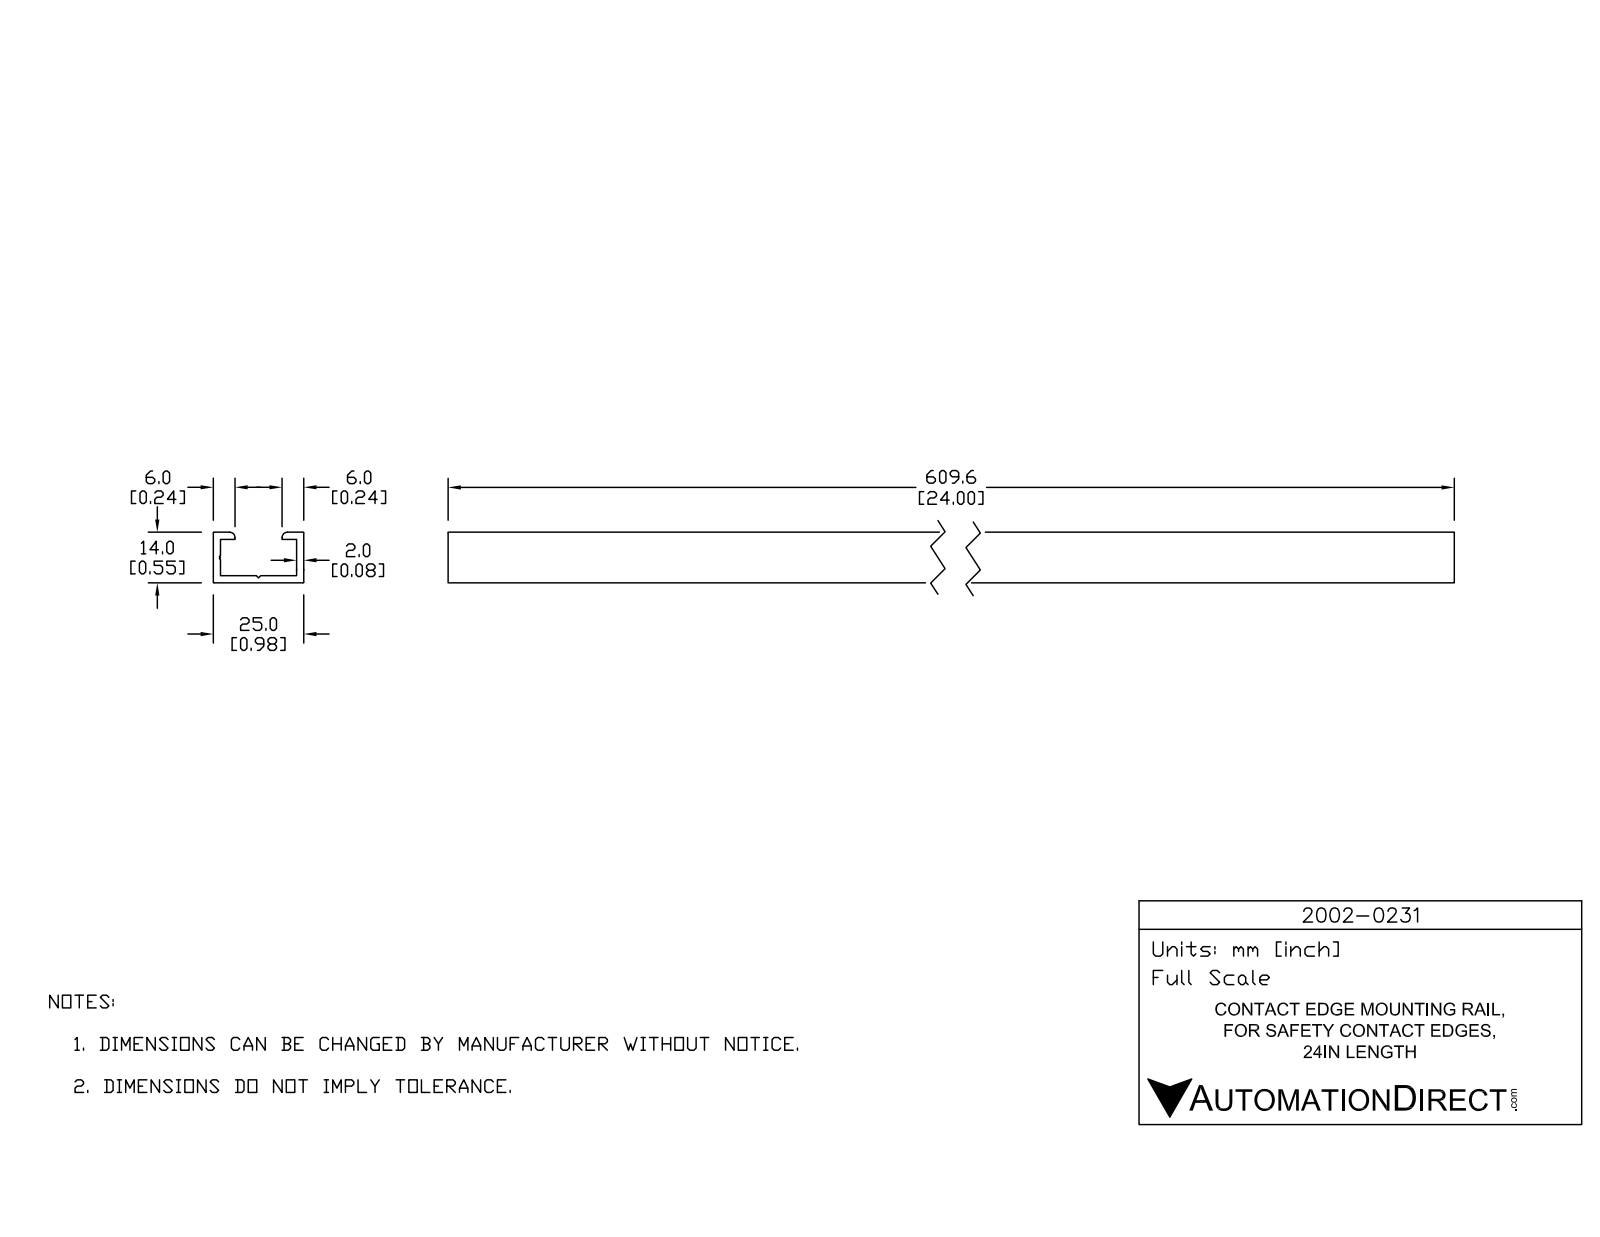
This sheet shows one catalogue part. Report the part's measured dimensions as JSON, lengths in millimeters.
{"part_name": "2002-0231", "step_written_by": "SolidWorks 2017 (AUTOMOTIVE_DESIGN)", "units": "millimeters", "bodies": {"solids": 1, "faces": 28, "planar": 22, "cylindrical": 6, "other": 0}, "overall_size": [6400.8, 25, 14], "volume_mm3": 719834, "surface_area_mm2": 751443, "partial_cylinders_radius": [[0.2, 4], [1.5, 2]], "face_to_face_distances": [2, 23, 12, 25, 21, 14, 10, 6, 19, 4]}
